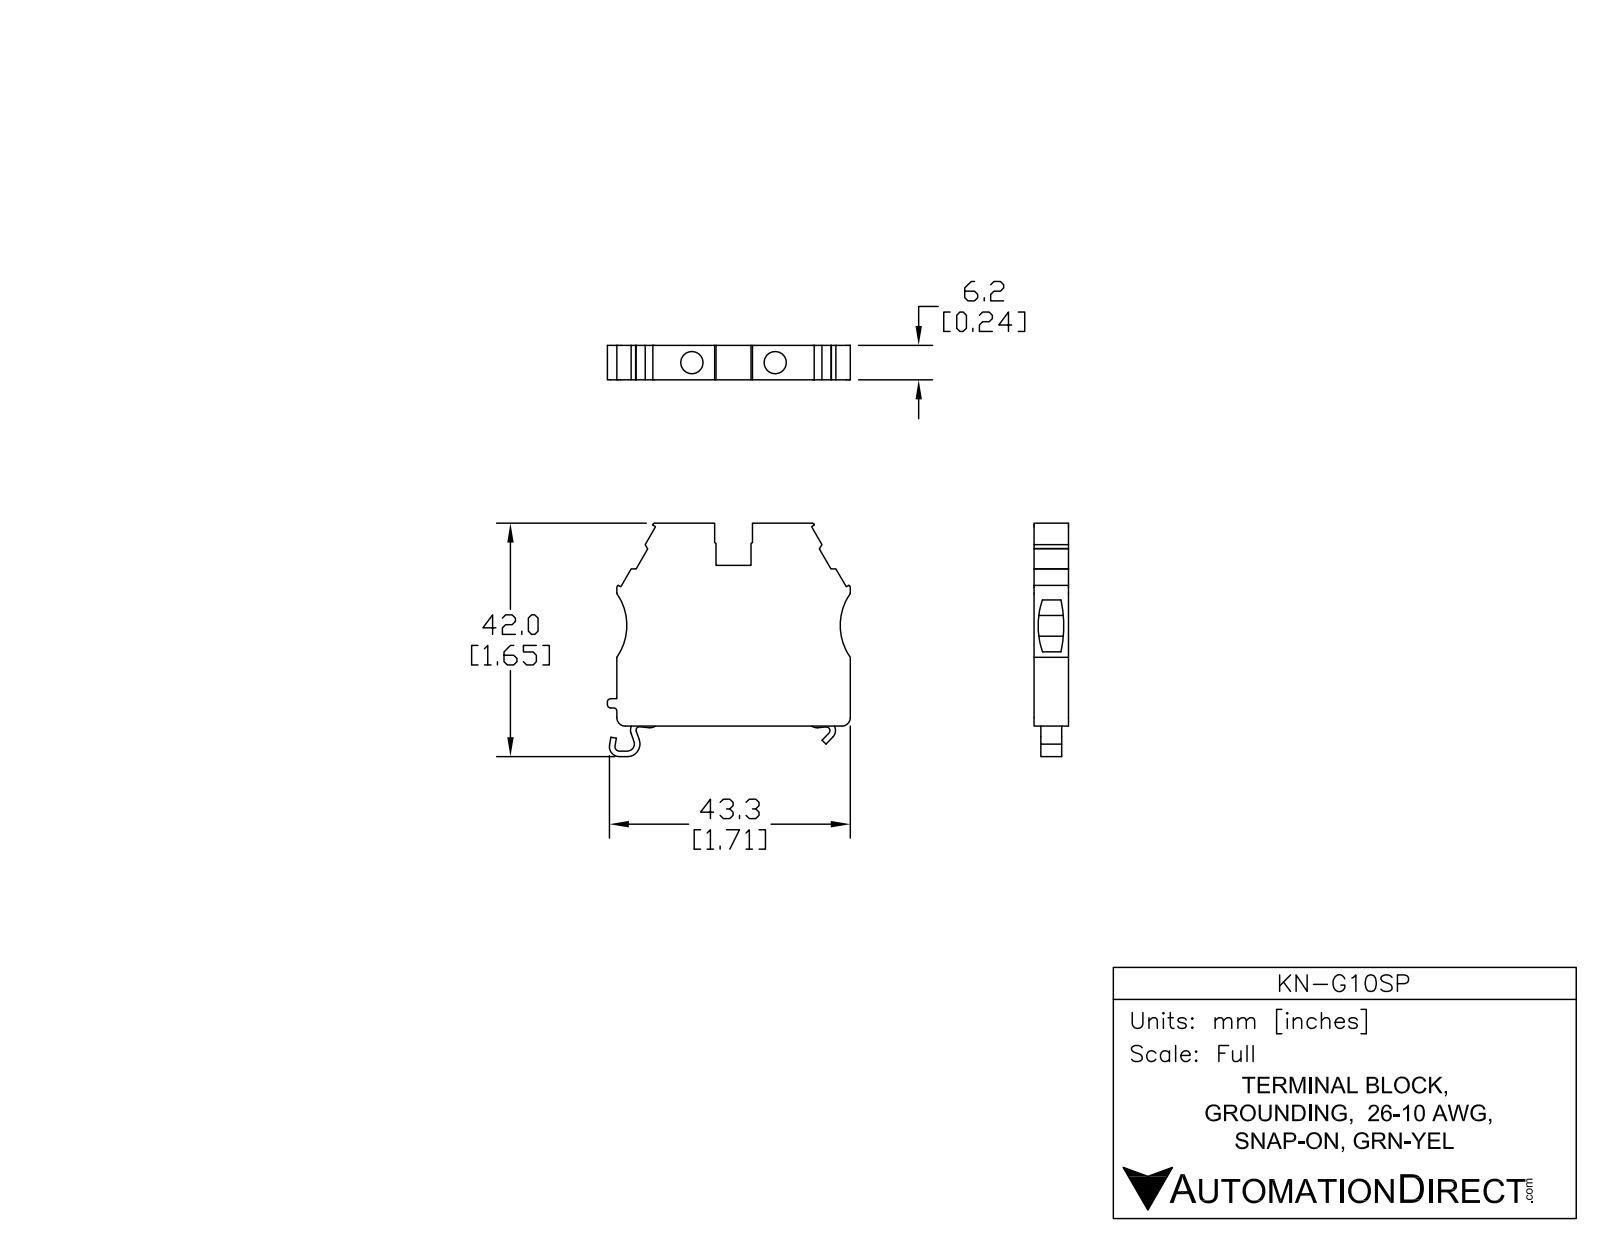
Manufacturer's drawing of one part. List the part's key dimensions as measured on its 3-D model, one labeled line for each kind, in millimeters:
Part name (STEP PRODUCT): KN-G10SP
STEP written by: SolidWorks 2014 (AUTOMOTIVE_DESIGN)
Units: millimetres
Bodies: 3 solids, 116 faces (64 planar, 52 cylindrical, 0 other)
Overall size (bounding box): 43.7 × 42 × 6.2
Volume: 7 840 mm³ · Surface area: 4 466 mm²
Round holes (diameter × count): ⌀4 ×2
Partial cylindrical surfaces — rounded edges, fillets, slot ends (radius × count): R0.1 ×8, R0.2 ×4, R0.3 ×4, R1.5 ×4, R0.5 ×3, R0.6 ×3, R10 ×2, R0.66 ×1
Main face-to-face distances: 6.2, 36.5, 7.6, 42, 0.78, 17.85, 24.15, 17.6, 24.4, 6.55
Hole centre spacings: 15
